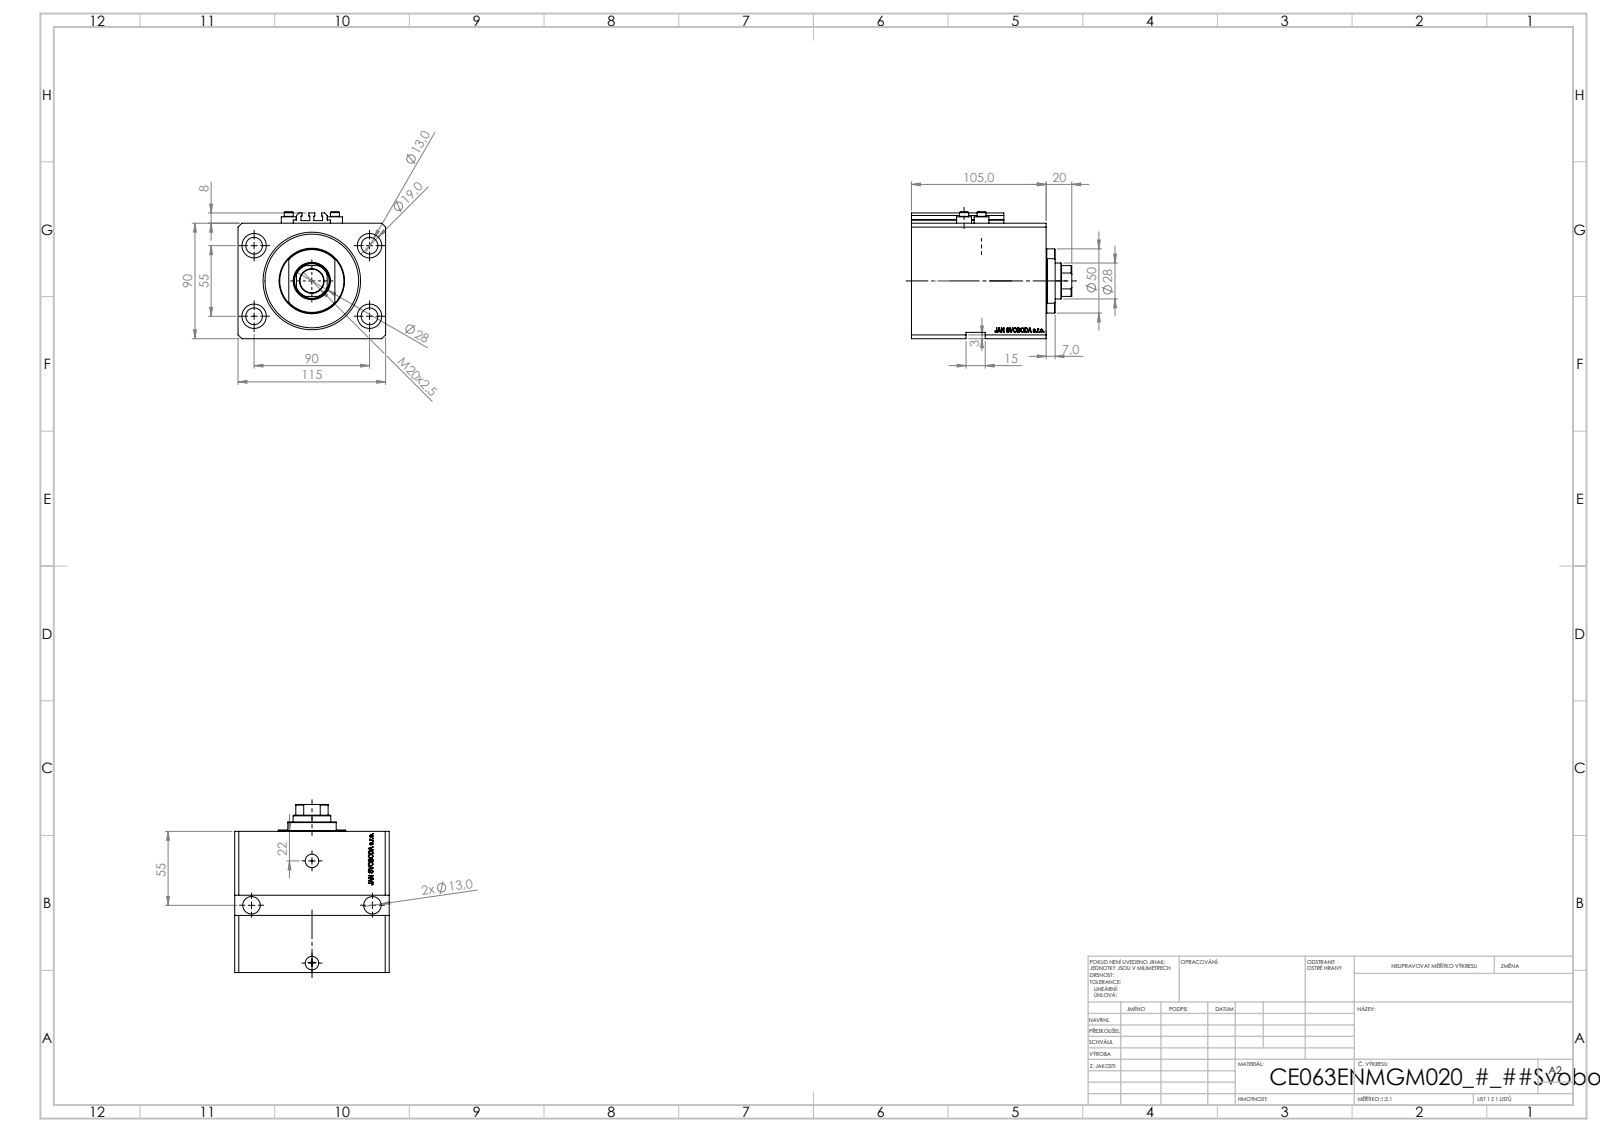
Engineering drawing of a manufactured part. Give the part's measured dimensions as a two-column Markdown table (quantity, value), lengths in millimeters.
| quantity | value |
| --- | --- |
| part name | V250CE_E_Body; V250CE_C_VCP; ALLEN BOLT V250CE; V250CE_VC_E |
| STEP written by | SolidWorks 2019 (CONFIG_CONTROL_DESIGN) |
| units | millimeters |
| bodies | 8 solids, 1107 faces (543 planar, 126 cylindrical, 438 other) |
| overall size | 125 × 115 × 99 |
| volume | 954 568 mm³ |
| surface area | 153 949 mm² |
| round holes (diameter × count) | 13 × 6, 1.25 × 4, 4 × 4, 19 × 4, 10 × 2, 13.16 × 2, 20 × 2, 18.5 × 1, 28 × 1, 63 × 1, 76 × 1 |
| round bosses / shafts (diameter × count) | 11.6 × 4, 7 × 4, 50 × 1 |
| partial cylindrical surfaces (radius × count) | 0.2 × 10, 13.5 × 1 |
| main face-to-face distances | 90, 20, 115, 85, 105, 87.1, 17.9, 67.1, 40, 65 |
| hole center spacings | 52.74, 55, 90, 13.6, 27.39, 28.46, 33.62, 36 |
